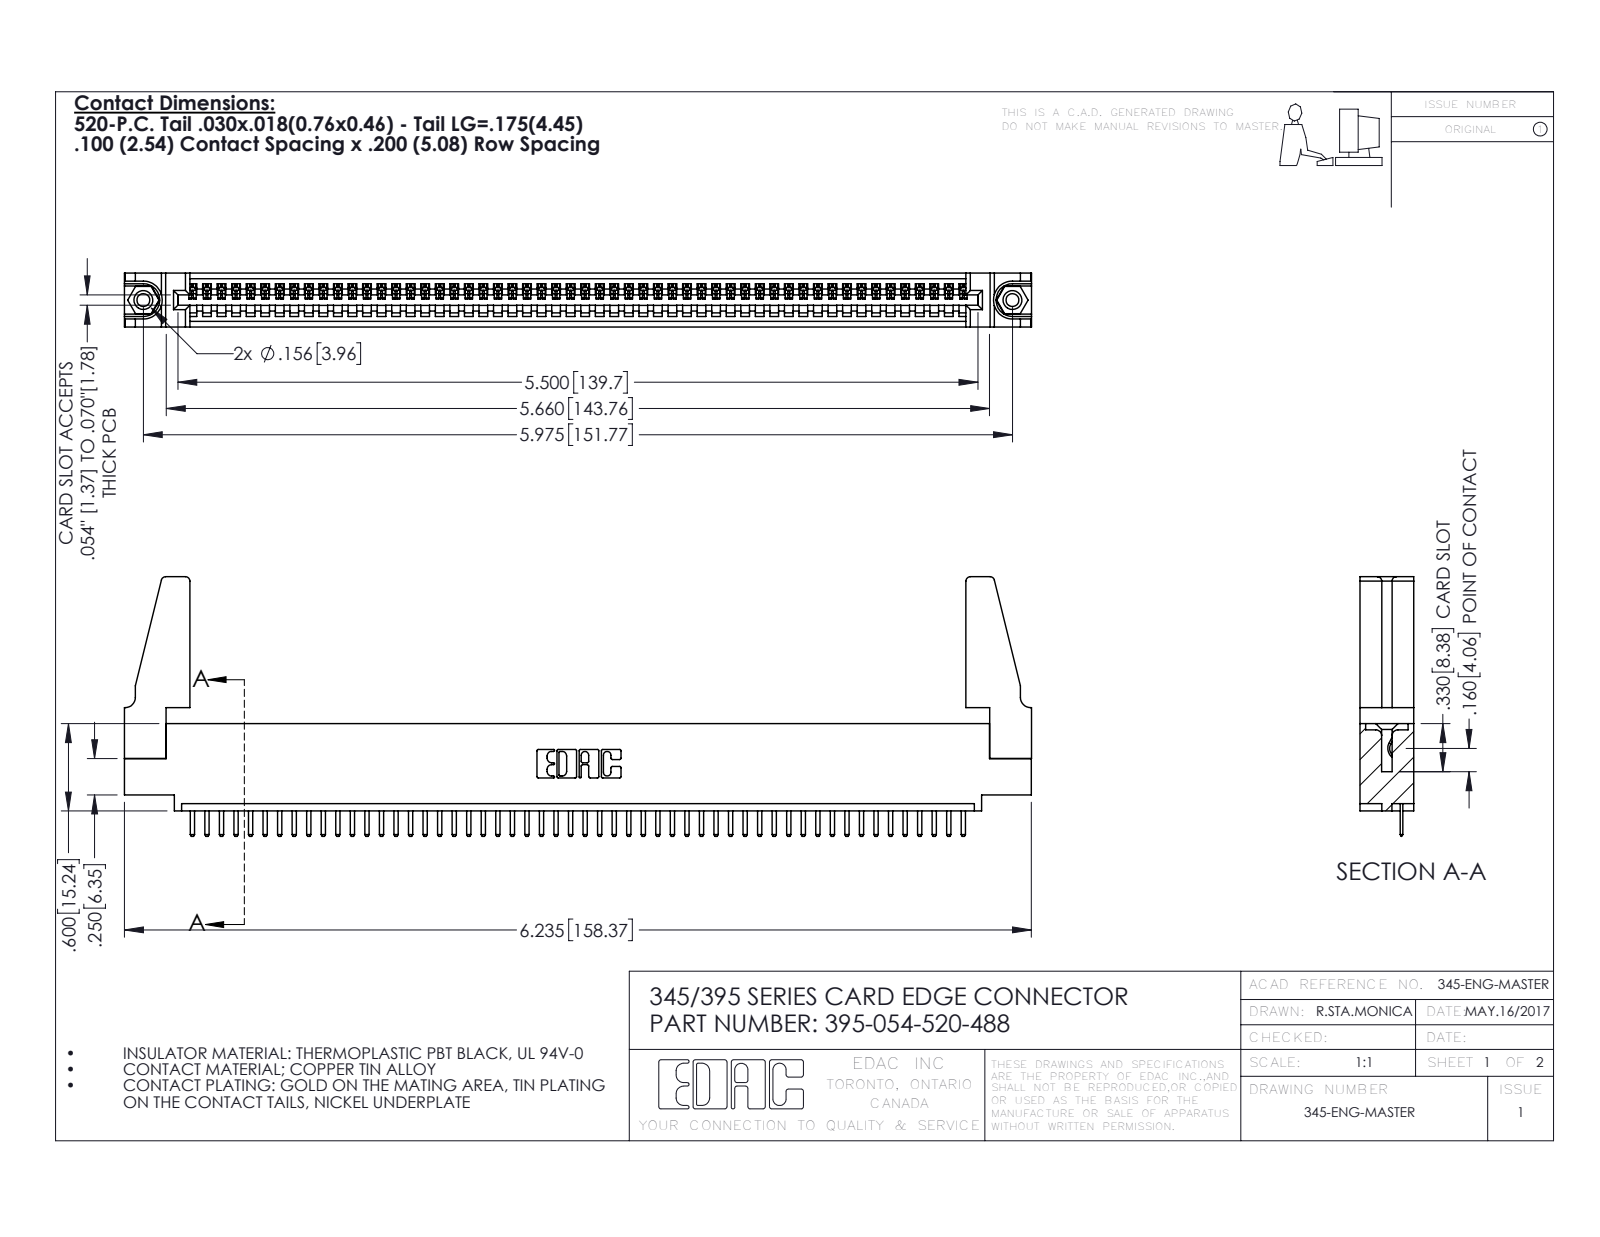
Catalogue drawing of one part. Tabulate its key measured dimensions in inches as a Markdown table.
| quantity | value |
| --- | --- |
| part name | 345-250-001_345-250-001-102; 345-220-078_345-220-088; 395-054-520-488; 345-292-001_345-293-120 (+1 more) |
| STEP written by | SolidWorks 2016 (CONFIG_CONTROL_DESIGN) |
| units | inches |
| bodies | 59 solids, 3602 faces (2424 planar, 1162 cylindrical, 16 other) |
| overall size | 6.236 × 1.785 × 0.37 |
| volume | 1.109 in³ |
| surface area | 35.16 in² |
| round holes (diameter × count) | 0.089 × 2, 0.125 × 2, 0.156 × 2, 0.064 × 1 |
| round bosses / shafts (diameter × count) | 0.155 × 2 |
| partial cylindrical surfaces (radius × count) | 0.01 × 110, 0.006 × 108, 0.01 × 22, 0.03 × 8, 0.007 × 6, 0.031 × 6, 0.026 × 3, 0.031 × 2 |
| main face-to-face distances | 0.072, 0.298, 0.37, 0.2, 0.098, 0.272, 0.025, 0.225, 0.072, 0.149 |
| hole center spacings | 0.27, 5.739, 5.975 |
